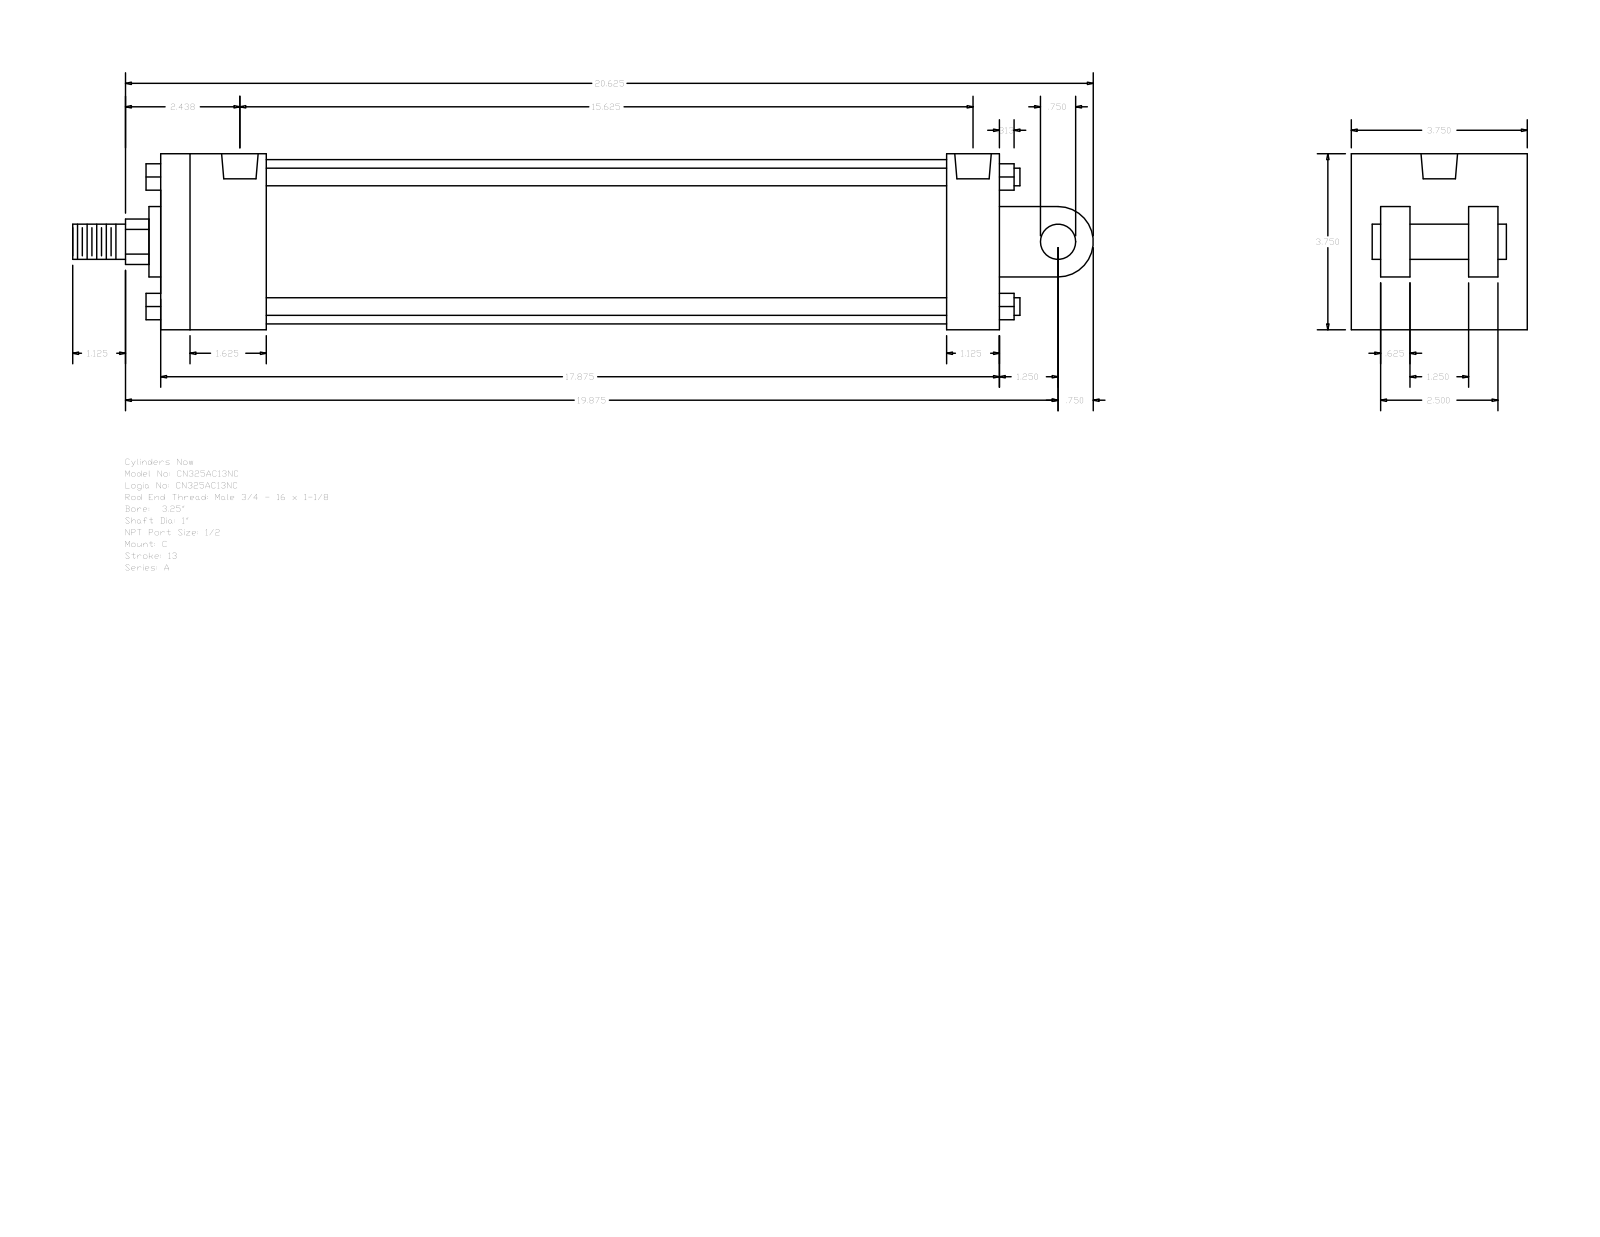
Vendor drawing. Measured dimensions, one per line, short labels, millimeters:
name: A_C__0325_1
written by: GSSL Pune (CONFIG_CONTROL_DESIGN)
unit: mm
bodies: 0 solids, 135 faces (102 planar, 33 cylindrical, 0 other)
size: 552.45 × 95.25 × 95.25
holes: 4× ⌀8.73, 2× ⌀19.77
bosses: 4× ⌀9.53, 2× ⌀19.05, 1× ⌀88.9, 1× ⌀38.1, 1× ⌀25.4
rounds: 1× R12.29, 1× R19.05
face distances: 95.24, 454.02, 15.87, 63.5, 28.57, 79.37, 31.74, 47.63, 66.67, 425.45
hole spacings: 3.18, 390.52, 393.7, 396.88
